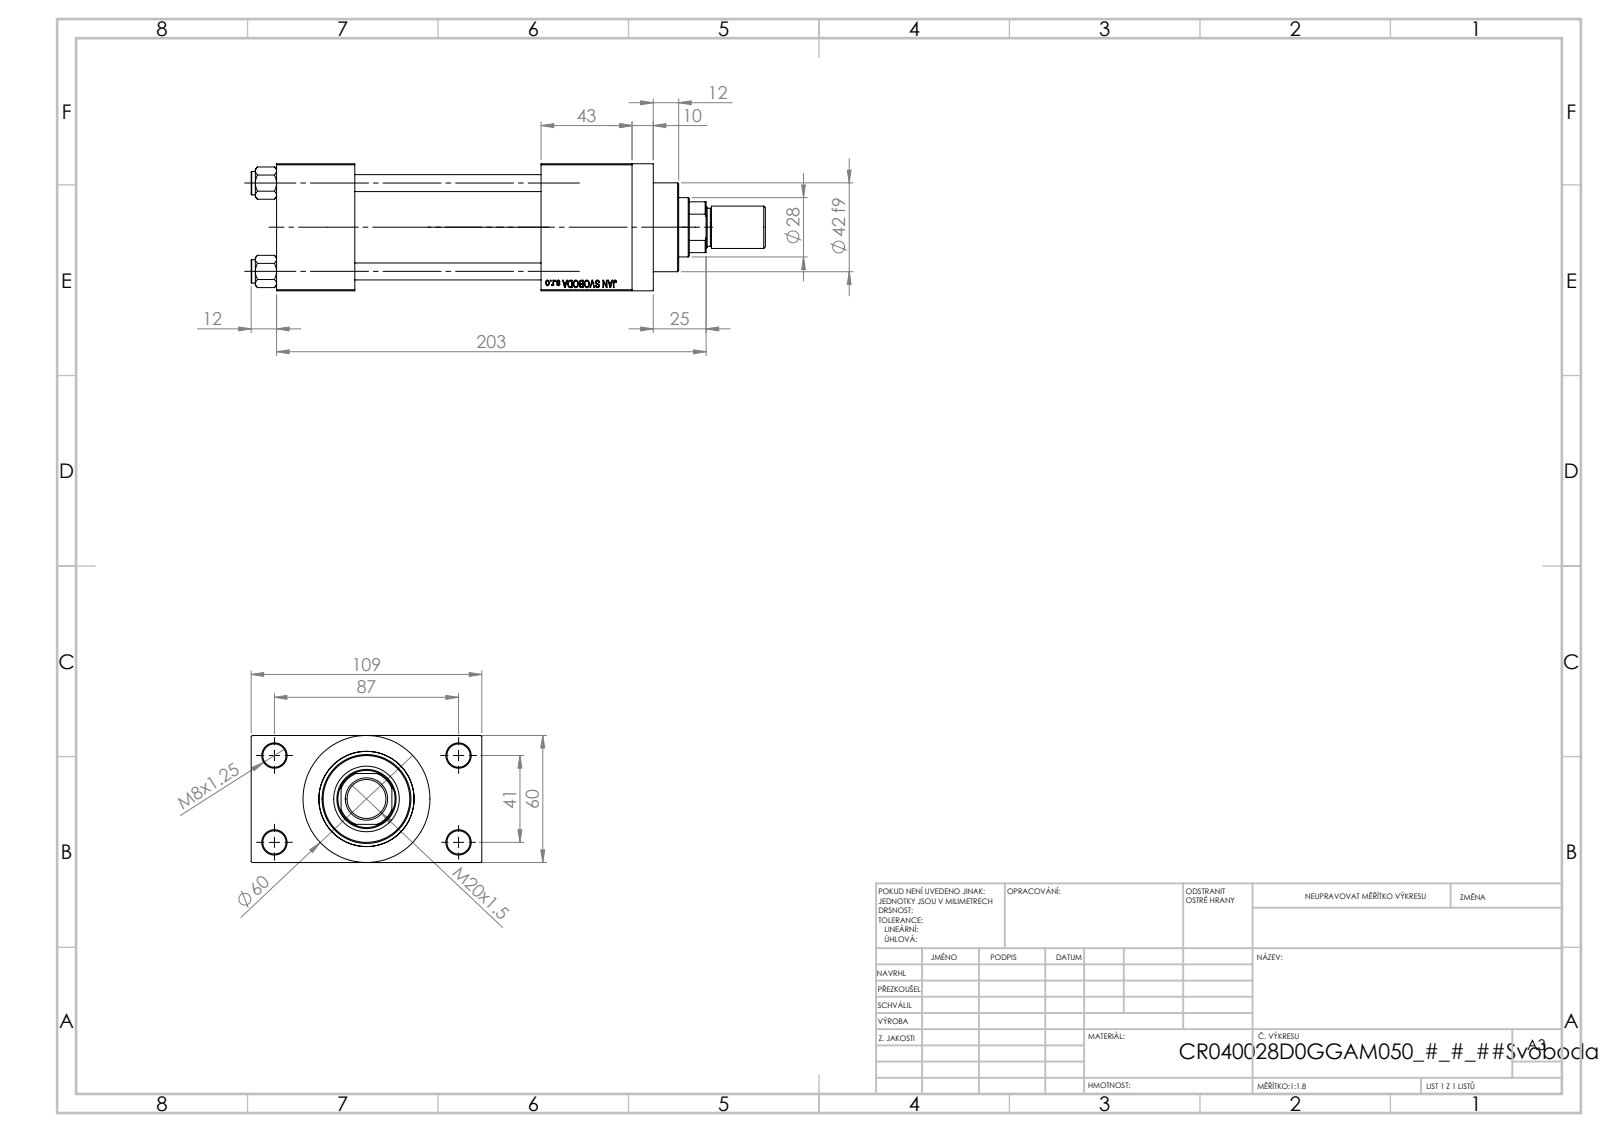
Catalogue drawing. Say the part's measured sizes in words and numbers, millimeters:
The part is named "NUT_M5_D; V215CR_VCP_D; V215CR_D_Body; ROD_END_AH (+2 more)". Its 3-D file was written by "SolidWorks 2019 (CONFIG_CONTROL_DESIGN)". It is 12 solids with 1119 faces: 502 planar, 93 cylindrical and 524 other. Overall it measures 243 by 109 by 60 millimeters. Its volume is 579 436 cubic millimeters and its surface area 144 020 square millimeters. Round holes: 4 of diameter 8, 4 of diameter 11, 2 of diameter 7, 2 of diameter 16.66, 2 of diameter 24, 1 of diameter 18.5, 1 of diameter 28, 1 of diameter 31, 1 of diameter 40, 1 of diameter 45. Round bosses or shafts: 4 of diameter 11, 1 of diameter 60, 1 of diameter 46, 1 of diameter 42, 1 of diameter 20, 1 of diameter 18. Partial cylindrical surfaces (rounded edges, fillets, slot ends): 1 of radius 13.5. The main face-to-face distances are 60, 24.5, 84.5, 88, 37, 125, 168, 131, 43, 109. The hole center spacings are 22.65, 29.49, 41.7, 47.15, 48.09, 64.35, 76.49, 41.
